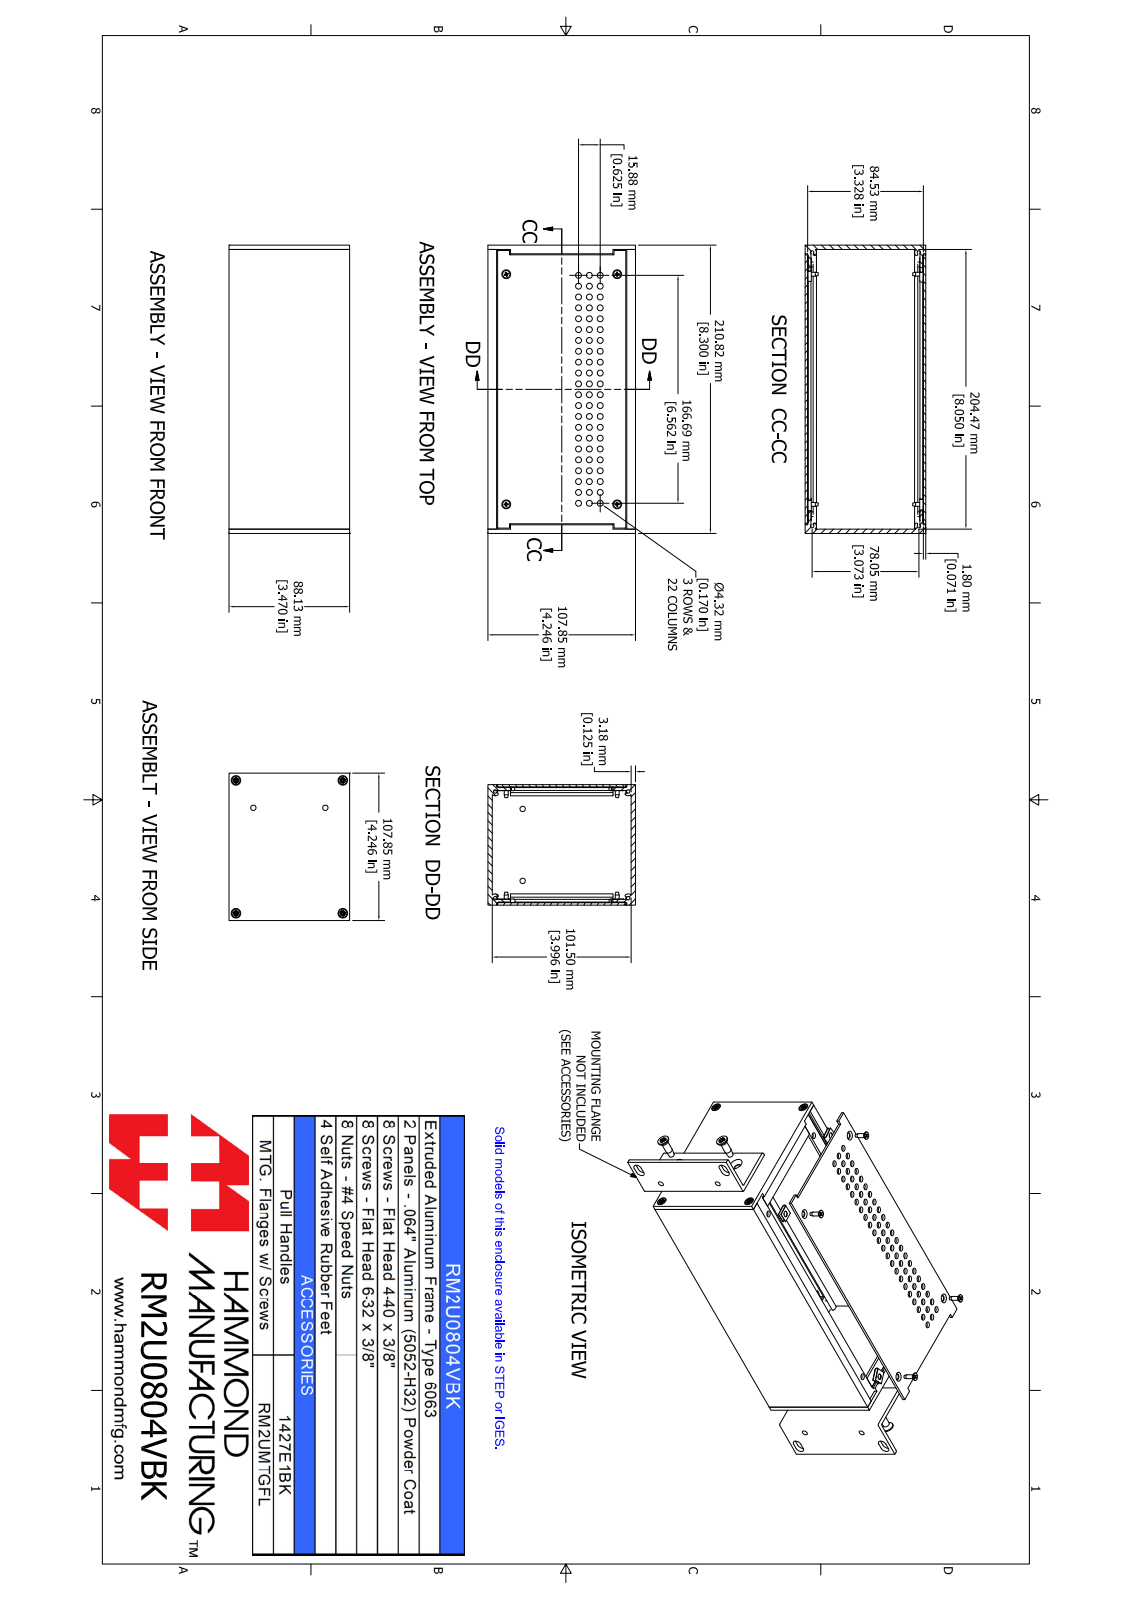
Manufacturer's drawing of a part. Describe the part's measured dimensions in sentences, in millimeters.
The part is named "RM2U0804VBK". Its 3-D file was written by "SolidWorks 2021 (AUTOMOTIVE_DESIGN)". It is 34 solids with 984 faces: 428 planar, 268 cylindrical and 288 other. Overall it measures 210.8 by 107.8 by 88.1 millimeters. Its volume is 288 200 cubic millimeters and its surface area 237 000 square millimeters. Round holes: 66 of diameter 4.3, 6 of diameter 2.5, 6 of diameter 4, 4 of diameter 3.5, 4 of diameter 4.3, 2 of diameter 4. Round bosses or shafts: 4 of diameter 6, 4 of diameter 5.4, 4 of diameter 3.5, 4 of diameter 2.8. Partial cylindrical surfaces (rounded edges, fillets, slot ends): 12 of radius 1, 12 of radius 1.2, 8 of radius 1.3, 8 of radius 3.2, 6 of radius 0.9, 5 of radius 1. The main face-to-face distances are 3.2, 1.8, 86.3, 104.7, 88.1, 107.8, 84.5, 101.5, 82.1, 4.2. The hole center spacings are 17.8, 8, 15.9, 25.1, 32.7, 7.9, 11.2, 23.8.
